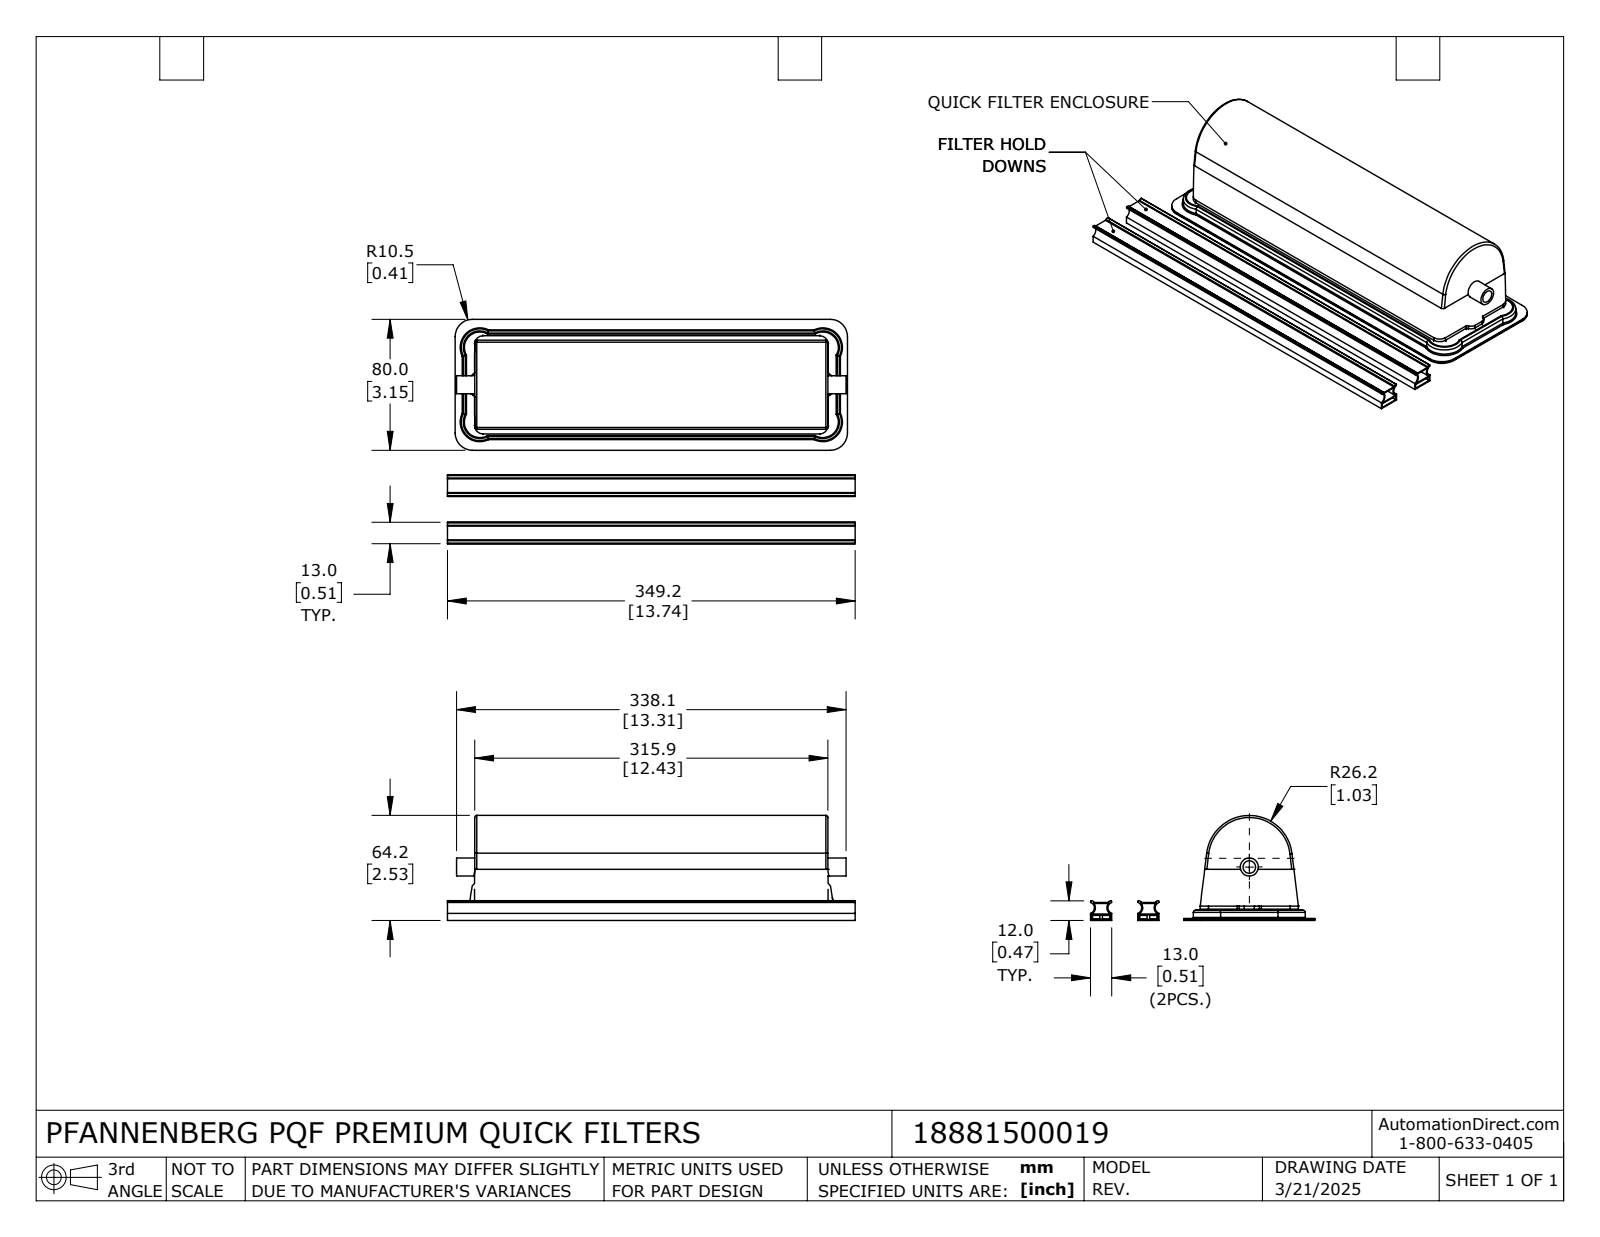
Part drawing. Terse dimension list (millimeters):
name: 18881500019
written by: SolidWorks 2024 (AUTOMOTIVE_DESIGN)
unit: mm
bodies: 12 solids, 427 faces (116 planar, 197 cylindrical, 114 other)
size: 349.3 × 137 × 64.2
volume: 715 000 mm³; area: 371 000 mm²
holes: 2× ⌀10.5, 1× ⌀7.7, 1× ⌀11
bosses: 8× ⌀1.6, 4× ⌀10.5, 2× ⌀11.8, 1× ⌀50.8
rounds: 42× R0.6, 42× R1.3, 8× R5, 4× R0.5, 4× R0.7, 4× R1.1, 4× R1.2, 4× R1.9
face distances: 0.6, 3.4, 2.7, 10.4, 7.1, 9.8, 5.7, 2.3, 4.7, 5
hole spacings: 235.2
